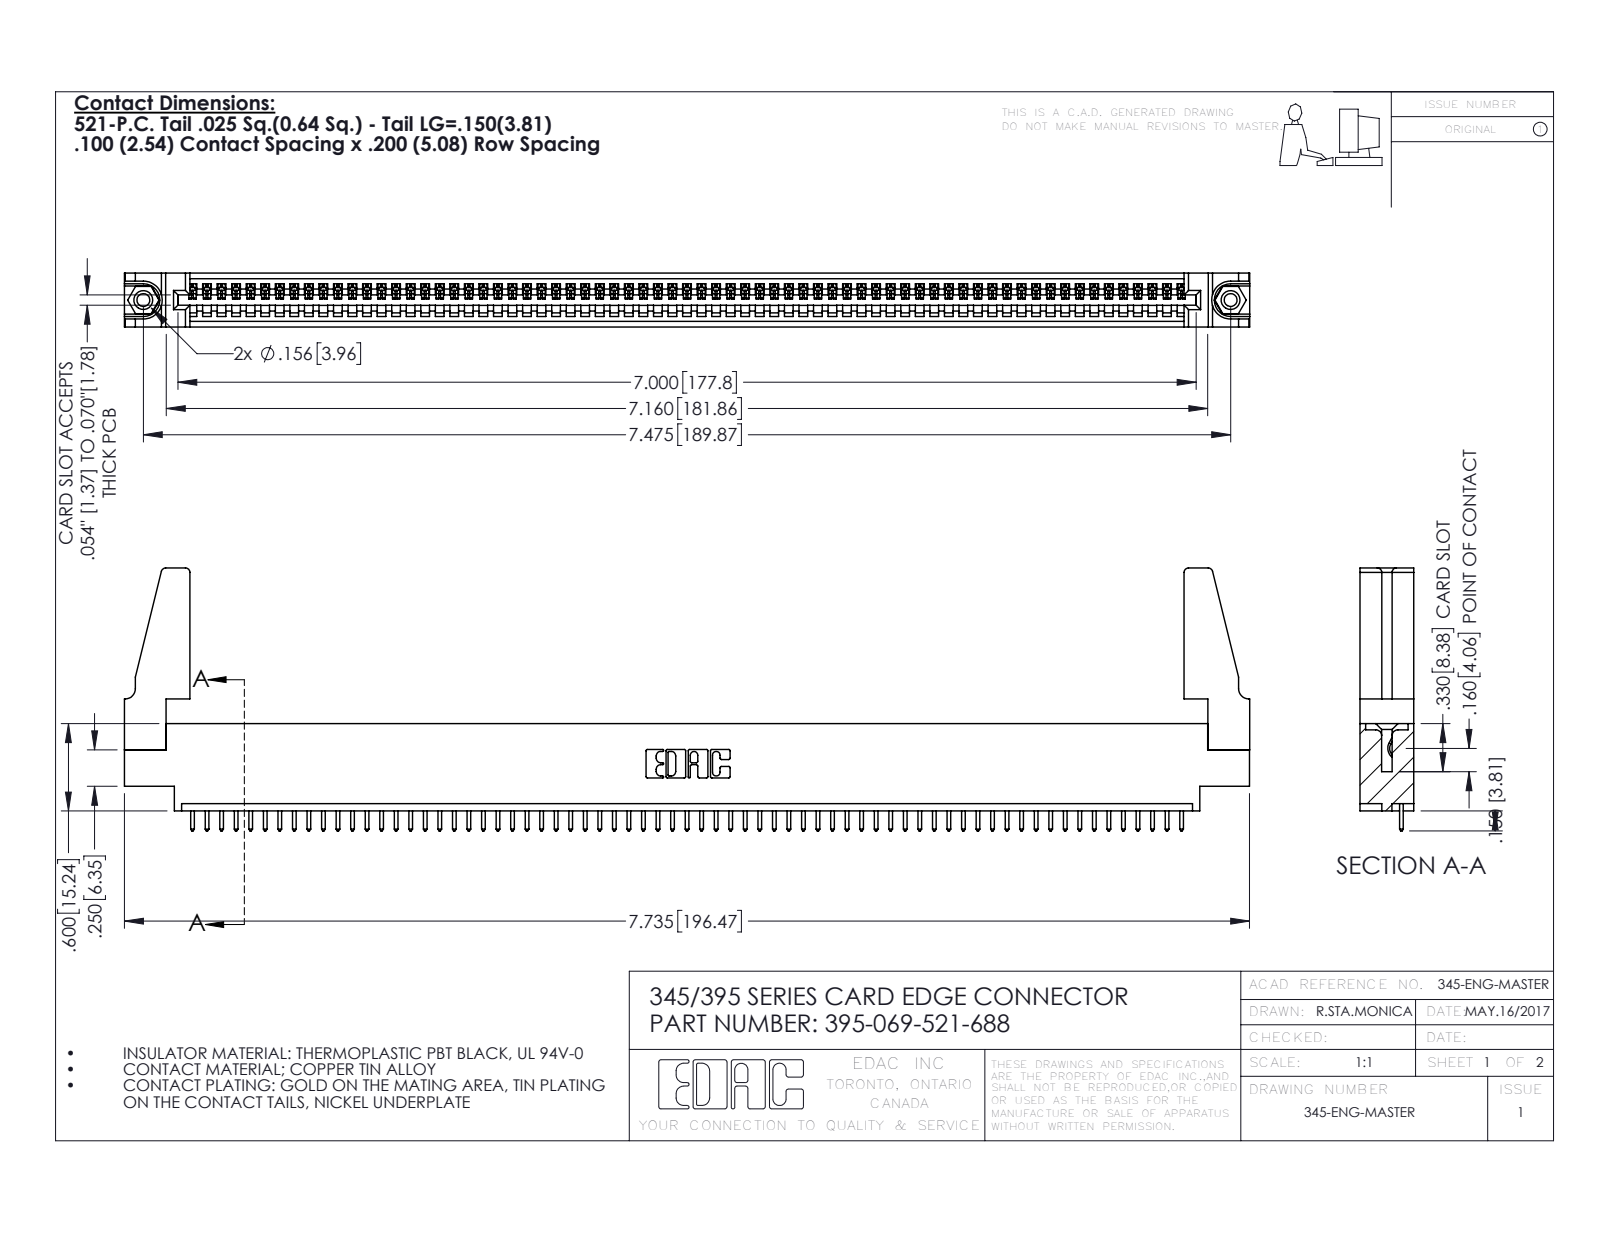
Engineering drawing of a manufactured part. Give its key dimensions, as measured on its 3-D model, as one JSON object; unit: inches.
{"part_name": "345-250-001_345-250-001-102; 345-292-001_345-293-121; 395-069-521-688; 345-220-078_345-220-088 (+1 more)", "step_written_by": "SolidWorks 2016 (CONFIG_CONTROL_DESIGN)", "units": "inches", "bodies": {"solids": 74, "faces": 4256, "planar": 2916, "cylindrical": 1324, "other": 16}, "overall_size": [7.736, 1.807, 0.37], "volume_in3": 1.332, "surface_area_in2": 42.69, "round_holes": [[0.089, 2], [0.125, 2], [0.156, 2], [0.064, 1]], "round_bosses_or_shafts": [[0.155, 2]], "partial_cylinders_radius": [[0.006, 138], [0.01, 138], [0.01, 22], [0.03, 8], [0.007, 6], [0.031, 6], [0.026, 3], [0.031, 2]], "face_to_face_distances": [0.072, 0.298, 0.37, 0.098, 0.272, 0.025, 0.2, 0.225, 0.175, 0.149], "hole_center_spacings": [0.27, 7.239, 7.475]}
